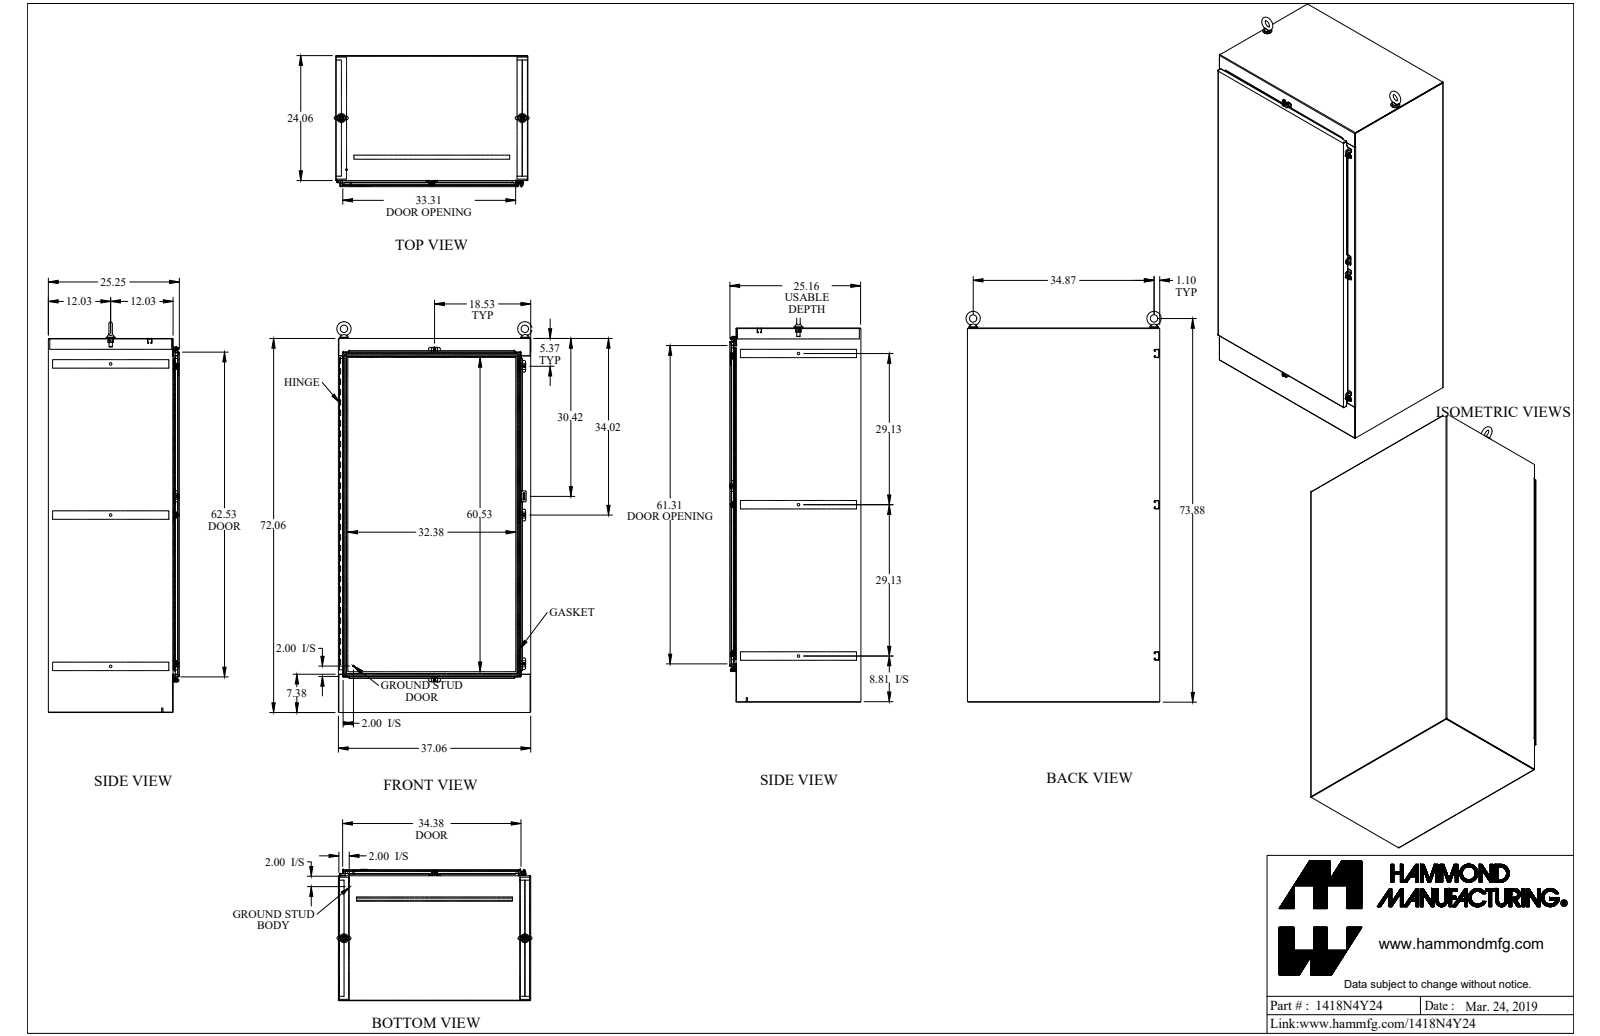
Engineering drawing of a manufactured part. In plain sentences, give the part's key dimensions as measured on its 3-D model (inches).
The part is named "1418N4Y24_Default". Its 3-D file was written by "SolidWorks 2019 (CONFIG_CONTROL_DESIGN)". It is 52 solids with 2017 faces: 1074 planar, 847 cylindrical and 96 other. Overall it measures 75.713 by 38.118 by 25.31 inches. Its volume is 1 188 cubic inches and its surface area 25 177 square inches. Round holes: 10 of diameter 0.304, 5 of diameter 0.213, 5 of diameter 0.375, 3 of diameter 0.265, 3 of diameter 0.5, 2 of diameter 0.265, 2 of diameter 0.527, 2 of diameter 0.687, 2 of diameter 0.75, 1 of diameter 0.11, 1 of diameter 0.125, 1 of diameter 0.625. Round bosses or shafts: 5 of diameter 0.5, 5 of diameter 0.39, 5 of diameter 0.244, 2 of diameter 1.75, 2 of diameter 1.5, 2 of diameter 1.25, 2 of diameter 0.738, 2 of diameter 0.281. Partial cylindrical surfaces (rounded edges, fillets, slot ends): 60 of radius 0.043, 54 of radius 0.138, 45 of radius 0.048, 45 of radius 0.143, 26 of radius 0.25, 10 of radius 0.06, 10 of radius 0.141, 8 of radius 0.125. The main face-to-face distances are 0.095, 25.152, 36.965, 25.057, 25.247, 36.87, 71.965, 37.06, 1.187, 23.965. The hole center spacings are 6, 12, 18, 24, 30, 36, 42, 29.13.
